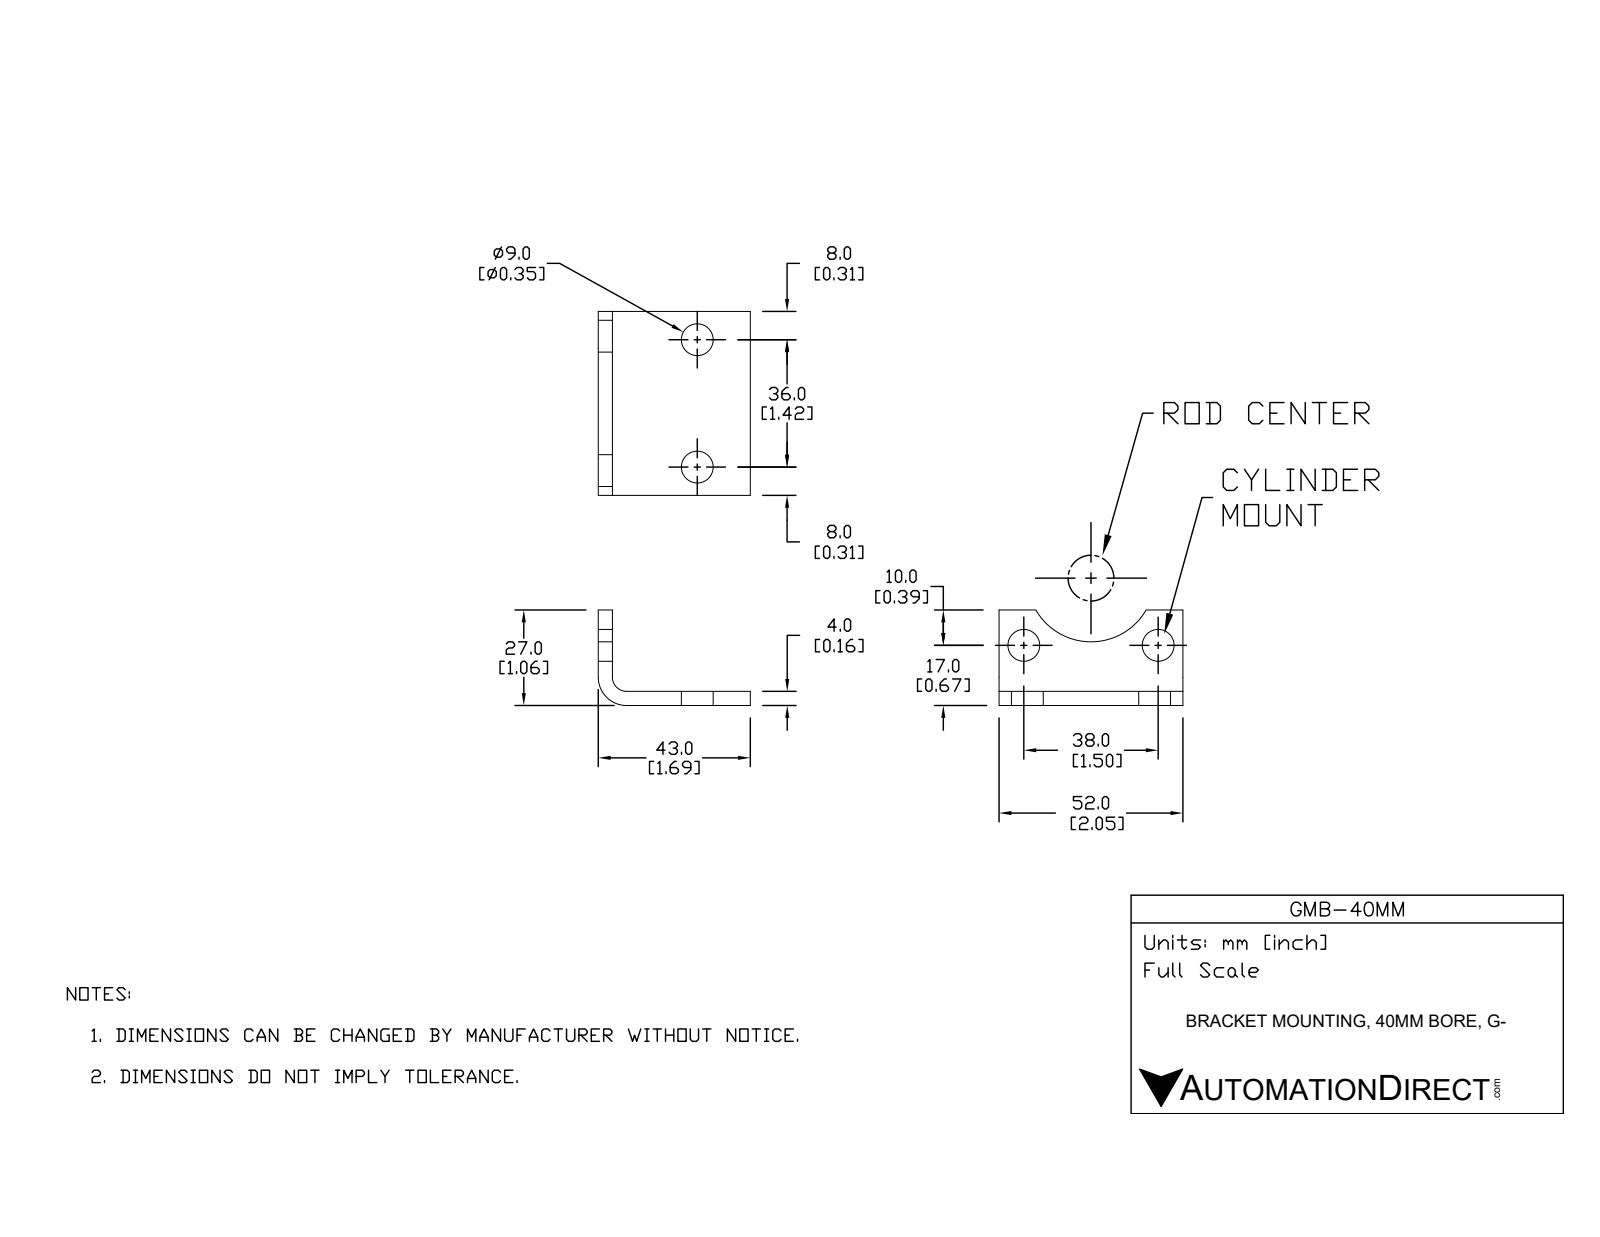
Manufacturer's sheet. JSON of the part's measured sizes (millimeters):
{"part_name": "GMB-40MM", "step_written_by": "SolidWorks 2017 (AUTOMOTIVE_DESIGN)", "units": "millimeters", "bodies": {"solids": 1, "faces": 24, "planar": 13, "cylindrical": 11, "other": 0}, "overall_size": [52, 43, 27], "volume_mm3": 11646, "surface_area_mm2": 7235, "round_holes": [[9, 4]], "partial_cylinders_radius": [[1, 1], [5, 1], [18, 1]], "face_to_face_distances": [4, 52, 43, 39, 27, 23], "hole_center_spacings": [36, 38]}
